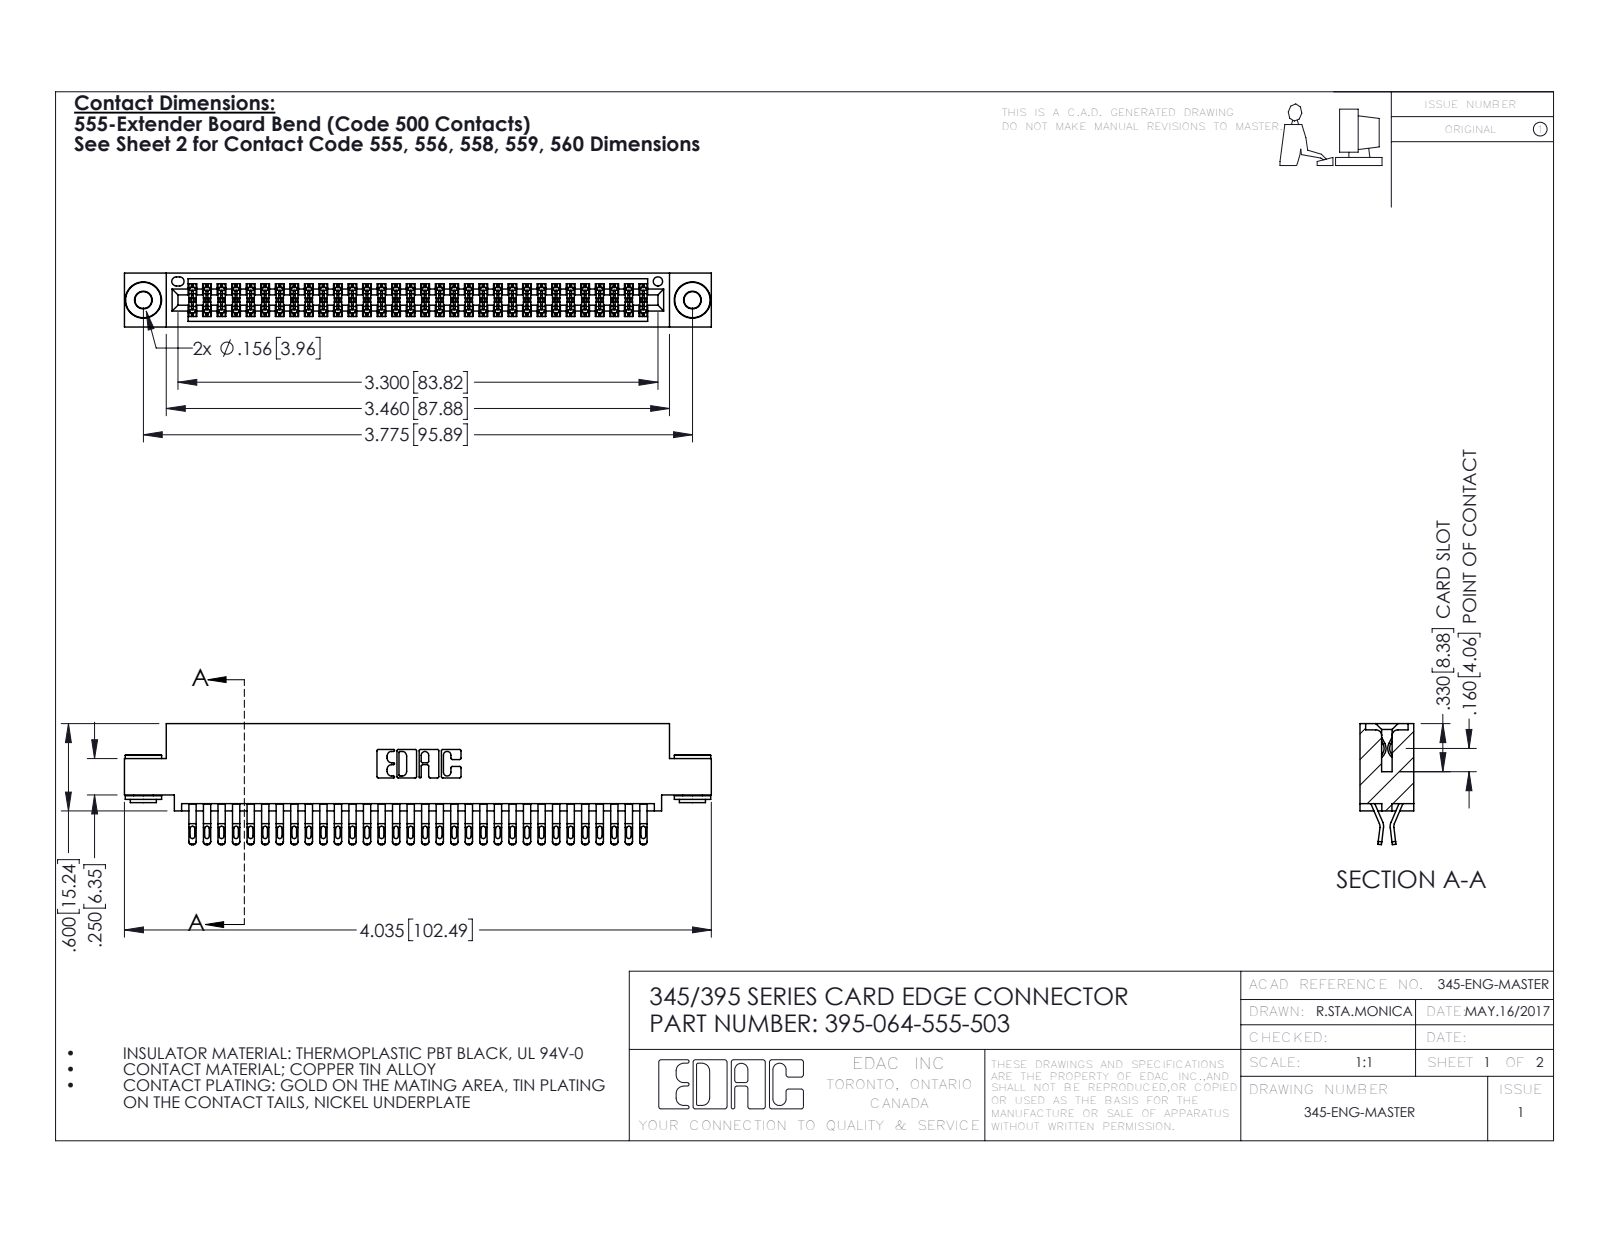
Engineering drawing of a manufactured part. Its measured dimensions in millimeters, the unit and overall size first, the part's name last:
Units: millimetres
Overall size (bounding box): 102.5 × 21.1 × 9.4
Round holes (diameter × count): ⌀2.9 ×2, ⌀4 ×2, ⌀1.6 ×1
Round bosses / shafts (diameter × count): ⌀6.4 ×2, ⌀4.6 ×2, ⌀3.5 ×2
Partial cylindrical surfaces — rounded edges, fillets, slot ends (radius × count): R0.4 ×160, R0.5 ×128, R0.2 ×96, R0.3 ×22, R0.2 ×6, R0.8 ×6, R0.7 ×3, R0.3 ×2
Main face-to-face distances: 1.8, 7.6, 0.6, 9.4, 5.1, 2.5, 6.9, 5.7, 4.4, 3.8
Hole centre spacings: 6.9, 89.9, 95.9
Volume: 10 000 mm³ · Surface area: 15 520 mm²
Bodies: 67 solids, 3752 faces (2078 planar, 1666 cylindrical, 8 other)
Part name (STEP PRODUCT): 345 Part_0.110 Offset - 0.156 Dia-TH; 345-250-002_345-250-002-102; 345-292-001_555 Tail; 395-064-555-503
STEP written by: SolidWorks 2016 (CONFIG_CONTROL_DESIGN)
